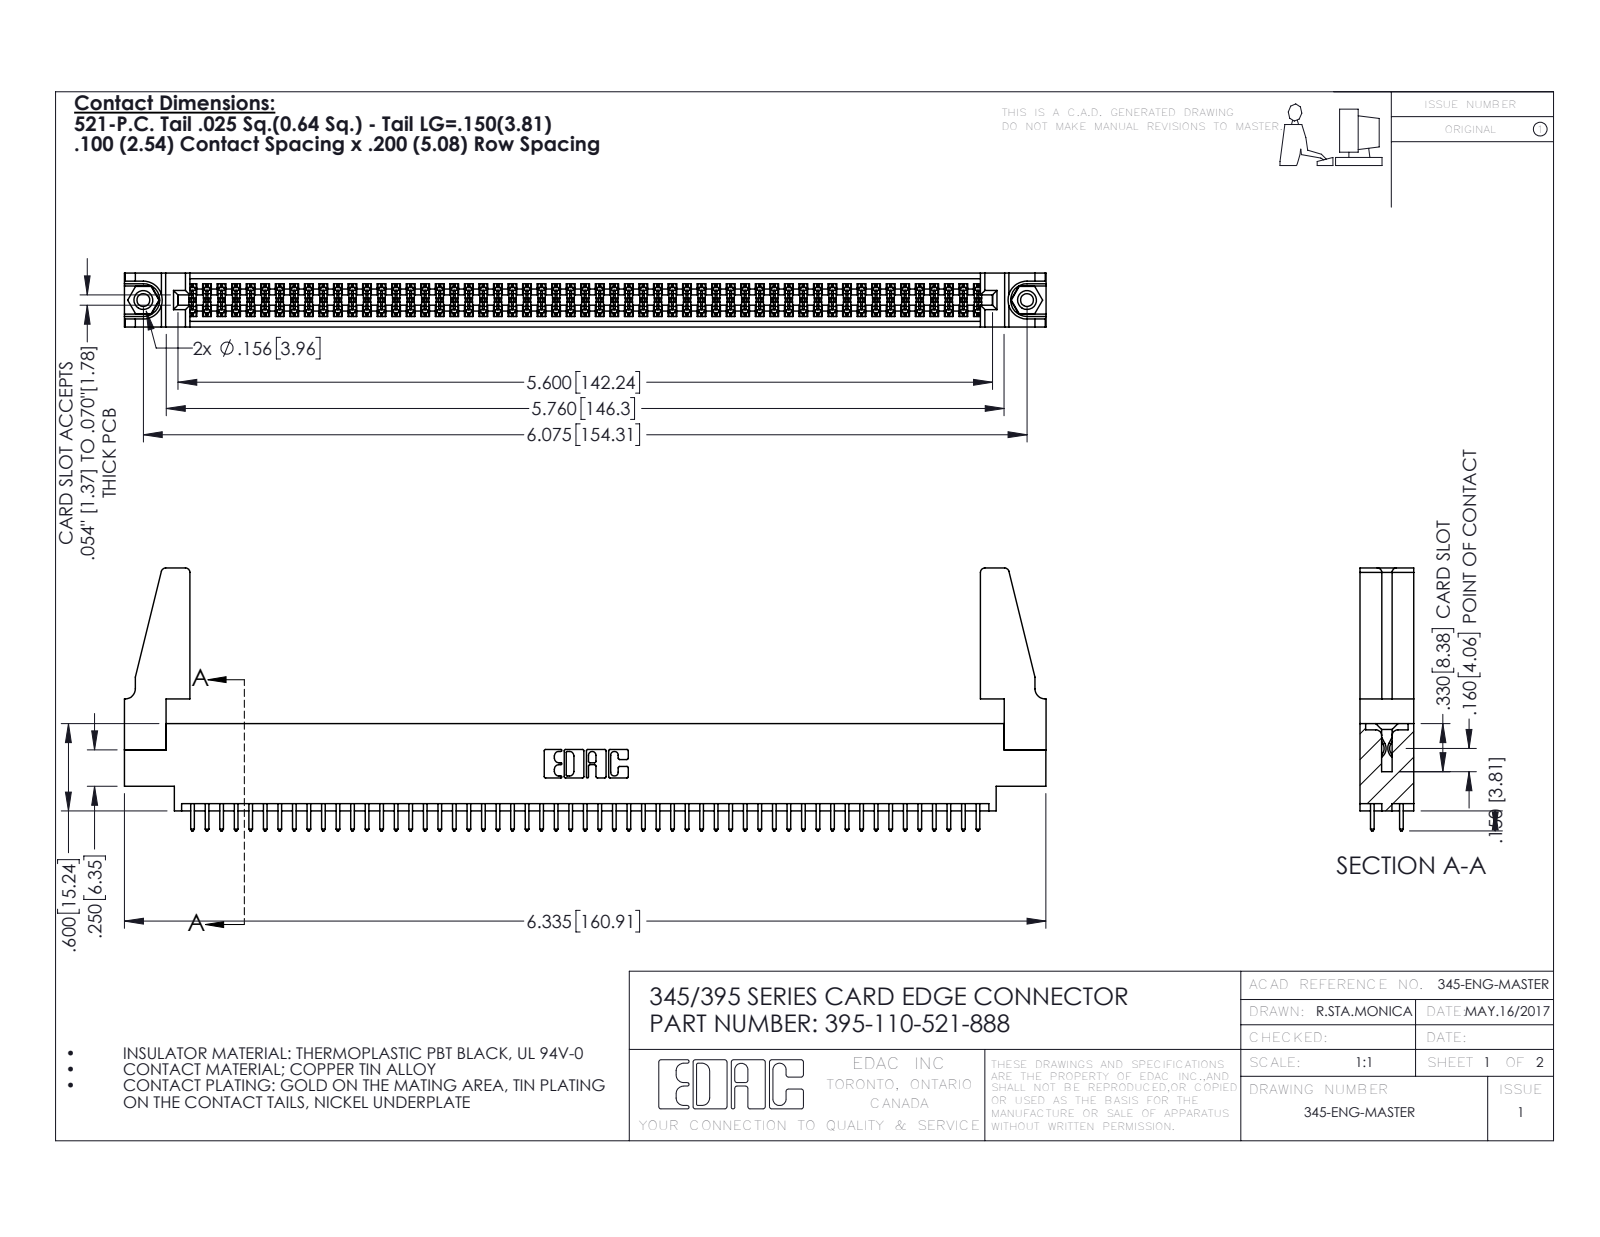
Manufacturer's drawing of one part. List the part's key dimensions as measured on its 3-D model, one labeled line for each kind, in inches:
Part name (STEP PRODUCT): 345-292-001_345-293-121; 345-250-001_345-250-001-102; 345-220-078_345-220-088; 345 Part_0.170 Offset - 0.156 Dia-TH (+1 more)
STEP written by: SolidWorks 2016 (CONFIG_CONTROL_DESIGN)
Units: inches
Bodies: 115 solids, 5754 faces (3786 planar, 1952 cylindrical, 16 other)
Overall size (bounding box): 6.336 × 1.807 × 0.37
Volume: 1.15 in³ · Surface area: 40.73 in²
Round holes (diameter × count): ⌀0.089 ×2, ⌀0.125 ×2, ⌀0.156 ×2, ⌀0.064 ×1
Round bosses / shafts (diameter × count): ⌀0.155 ×2
Partial cylindrical surfaces — rounded edges, fillets, slot ends (radius × count): R0.006 ×165, R0.01 ×110, R0.01 ×22, R0.03 ×8, R0.007 ×6, R0.031 ×6, R0.026 ×3, R0.014 ×2
Main face-to-face distances: 0.072, 0.298, 0.37, 0.2, 0.098, 0.272, 0.025, 0.225, 0.175, 0.149
Hole centre spacings: 0.27, 5.839, 6.075
